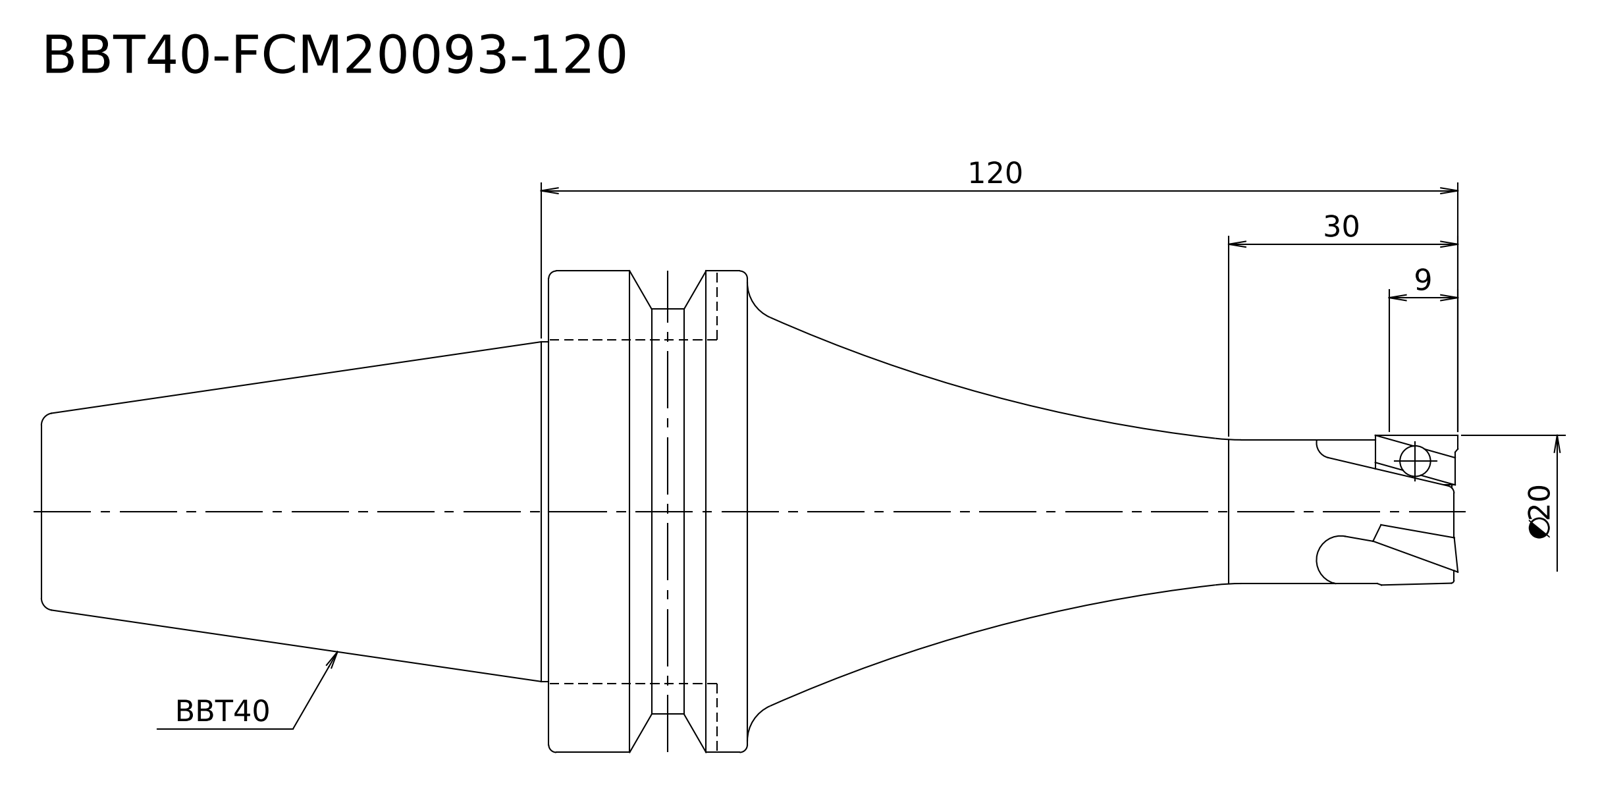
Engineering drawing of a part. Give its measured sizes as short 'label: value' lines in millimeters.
written by: Kubotek KeyCreator V8.5.1 (14335) (CONFIG_CONTROL_DESIGN)
unit: mm
bodies: 1 solid, 17 faces (4 planar, 6 cylindrical, 7 other)
size: 185.4 × 63 × 63
volume: 216 546 mm³; area: 25 553 mm²
bosses: 1× ⌀63, 1× ⌀53, 1× ⌀44.45, 1× ⌀20, 1× ⌀18.8
face distances: 66.4, 119, 185.4, 93, 26, 92.4
